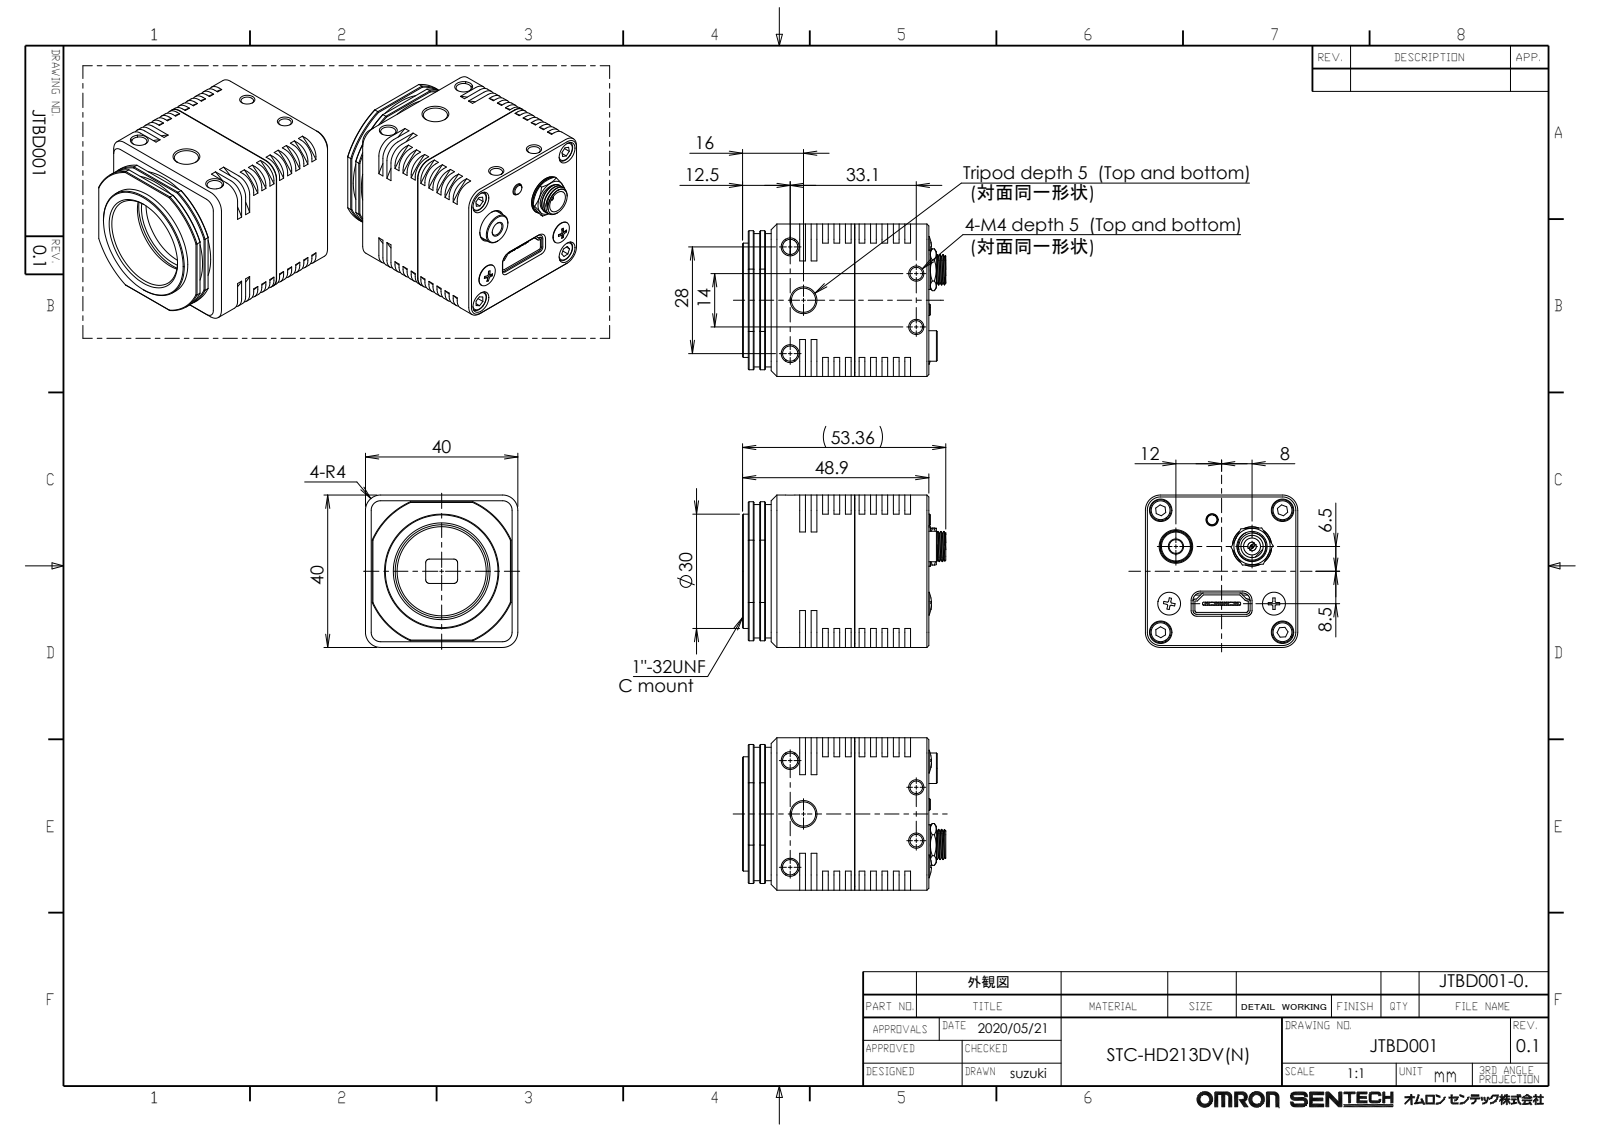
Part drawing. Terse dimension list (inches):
name: STC-HD213DV
written by: SolidWorks 2019 (AUTOMOTIVE_DESIGN)
unit: in
bodies: 18 solids, 1713 faces (1215 planar, 394 cylindrical, 104 other)
size: 2.101 × 1.575 × 1.575
volume: 3.669 in³; area: 41.42 in²
holes: 4× ⌀0.118, 4× ⌀0.122, 4× ⌀0.232, 3× ⌀0.126, 2× ⌀0.094, 2× ⌀0.13, 2× ⌀0.157, 1× ⌀0.142, 1× ⌀0.23, 1× ⌀0.25, 1× ⌀0.279, 1× ⌀0.312
bosses: 39× ⌀0.016, 4× ⌀0.217, 3× ⌀0.118, 2× ⌀0.236, 2× ⌀0.157, 2× ⌀0.031, 1× ⌀1.378, 1× ⌀1.181
rounds: 12× R0.126, 11× R0.039, 10× R0.012, 7× R0.02, 4× R0.01, 4× R0.024, 4× R0.157, 2× R0.005
face distances: 1.575, 0.059, 0.744, 0.118, 0.413, 0.472, 0.591, 0.177, 0.531, 0.236
hole spacings: 0.891, 1.26, 0.308, 0.406, 0.541, 0.568, 0.637, 0.969
